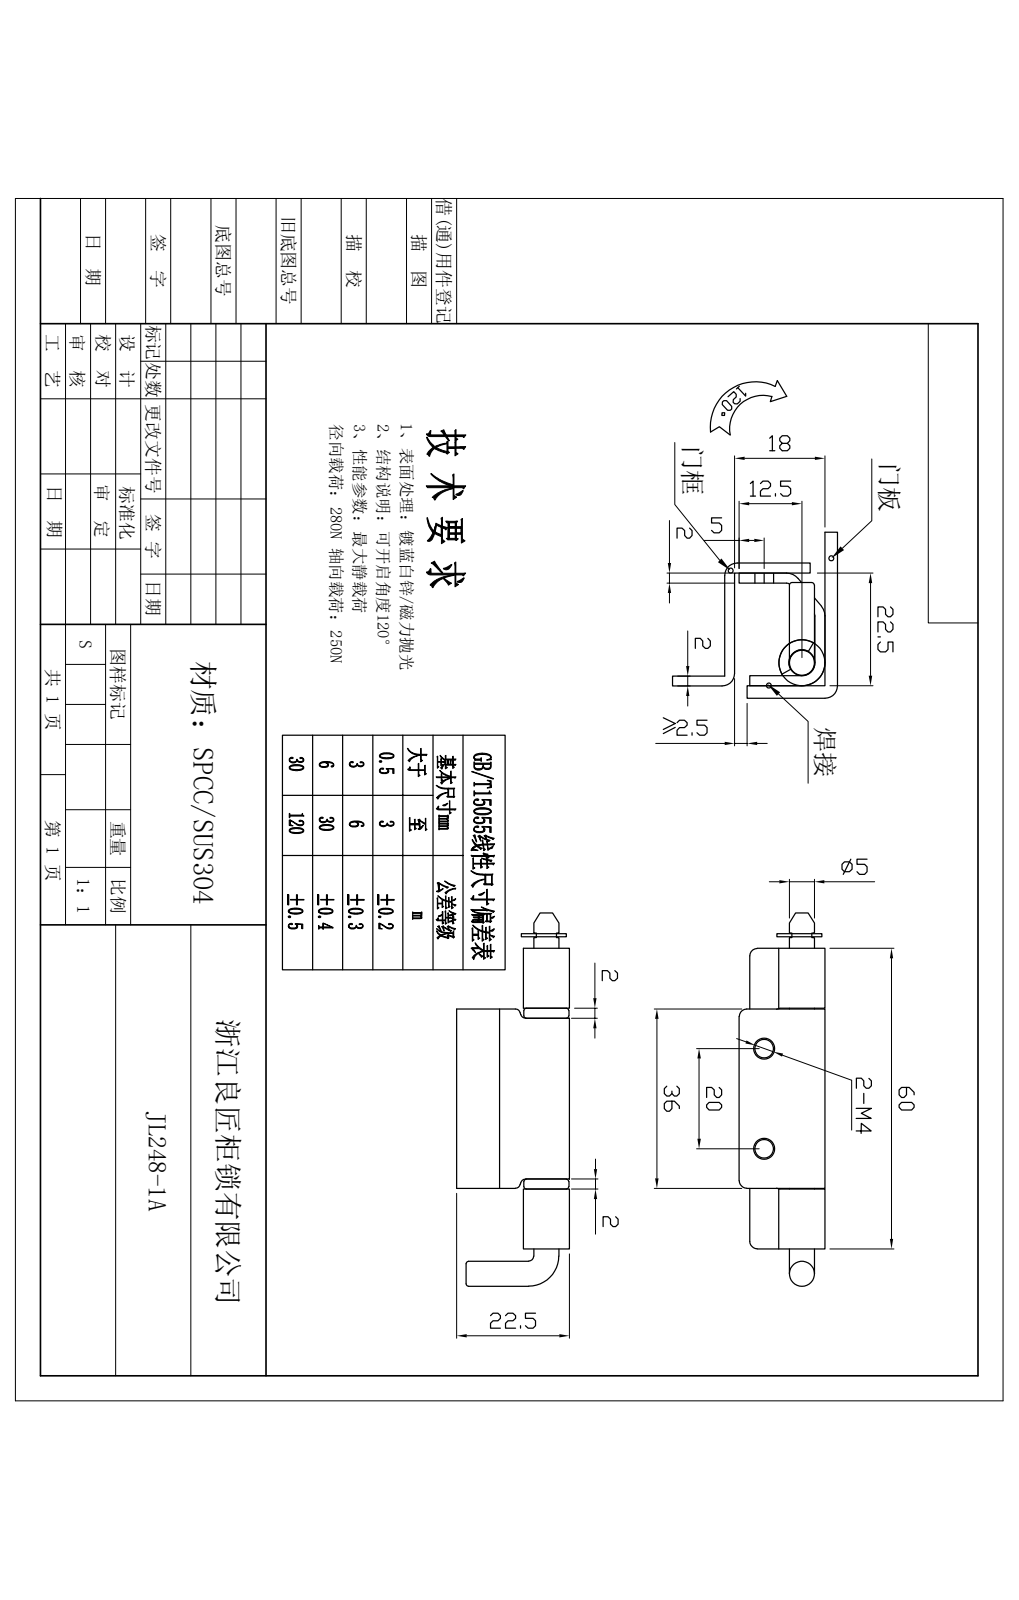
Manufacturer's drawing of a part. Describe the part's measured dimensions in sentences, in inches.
Its 3-D file was written by "Rhino 8.5 (CONFIG_CONTROL_DESIGN)". It is 6 solids with 116 faces: 36 planar, 58 cylindrical and 22 other. Overall it measures 2.933 by 0.909 by 0.673 inches. Its volume is 0.437 cubic inches and its surface area 12.02 square inches. Round holes: 2 of diameter 0.148, 2 of diameter 0.165, 1 of diameter 0.157, 1 of diameter 0.205. Round bosses or shafts: 2 of diameter 0.197, 1 of diameter 0.362, 1 of diameter 0.354. Partial cylindrical surfaces (rounded edges, fillets, slot ends): 8 of radius 0.059, 4 of radius 0.039, 4 of radius 0.059, 2 of radius 0.118. The main face-to-face distances are 0.079, 0.807, 0.886, 0.728, 0.093, 1.343, 0.591, 0.512, 0.47, 0.549. The hole center spacings are 0.787.
